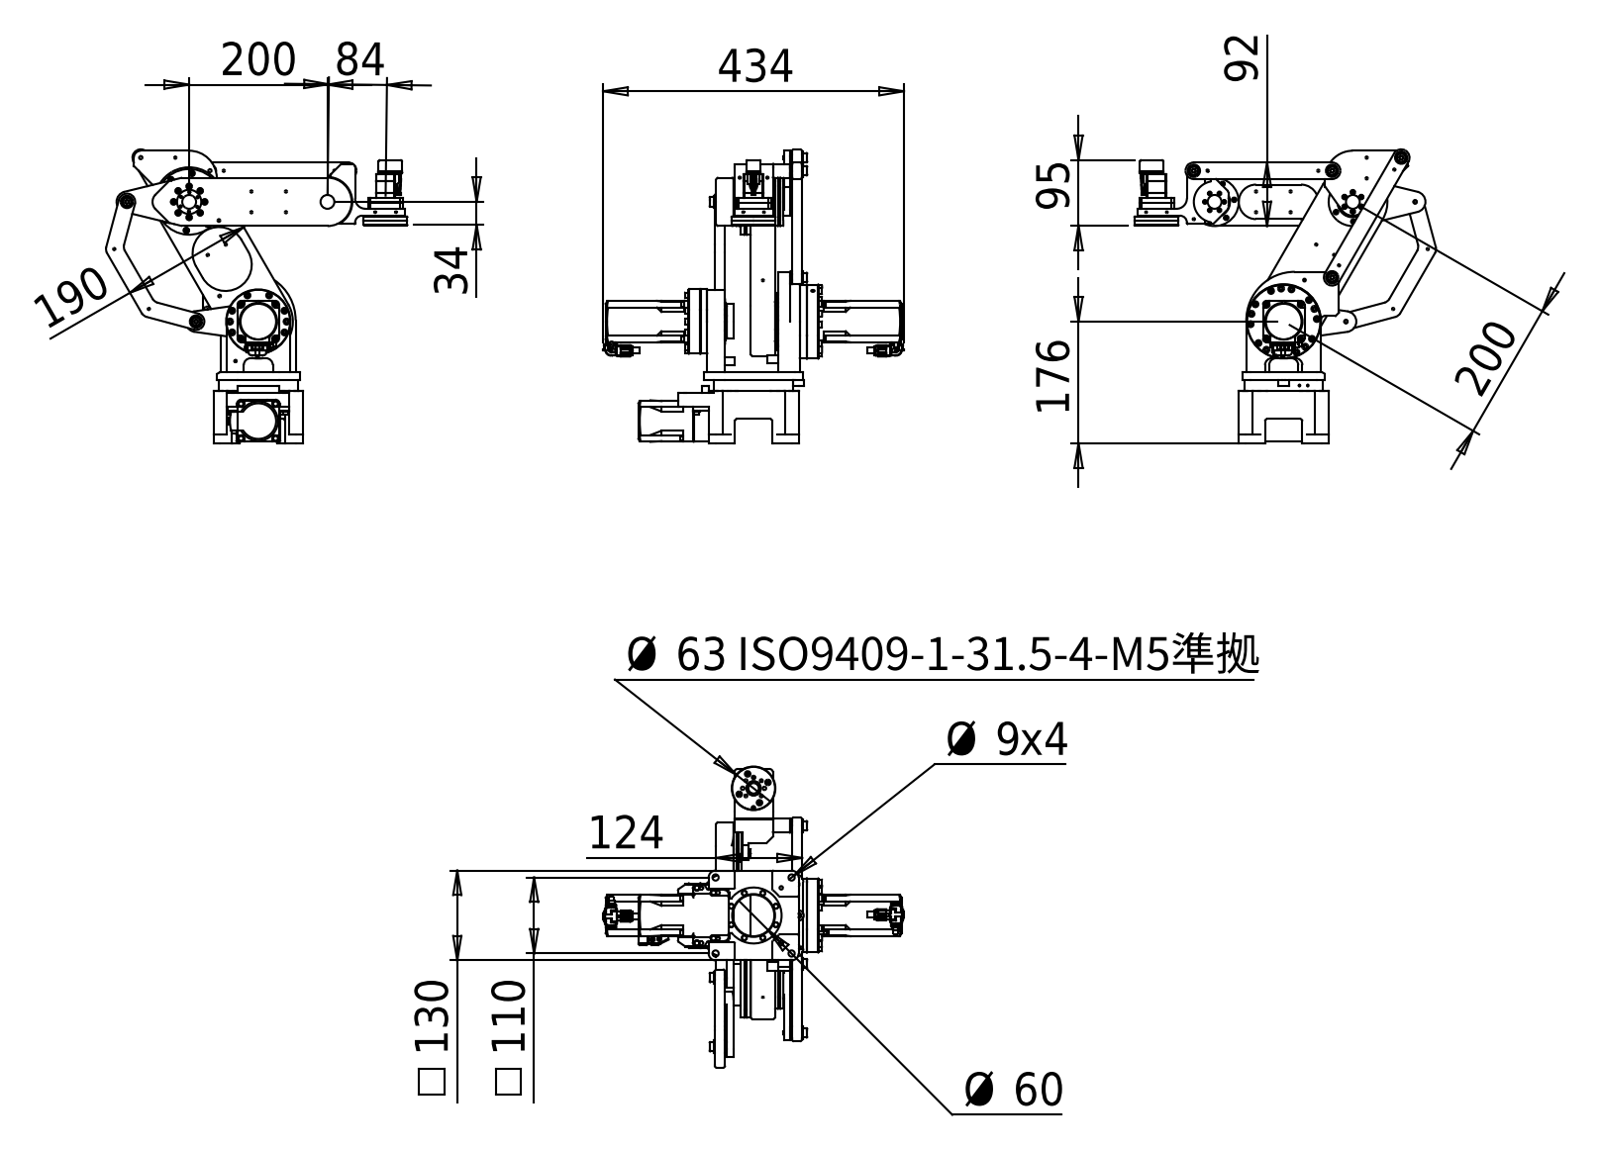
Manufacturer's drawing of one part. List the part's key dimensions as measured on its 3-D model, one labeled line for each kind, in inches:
Part name (STEP PRODUCT): UMBKS12_15_M4_3; SSRBN16_A; CRBFV3515ATUU_61; hexagon socket head cap screw_jis_JIS B 1176 M3 x 12 (12) --N (+8 more)
STEP written by: SolidWorks 2022 (AUTOMOTIVE_DESIGN)
Units: inches
Bodies: 313 solids, 11675 faces (4414 planar, 3799 cylindrical, 3462 other)
Overall size (bounding box): 25.501 × 17.794 × 17.118
Volume: 299.9 in³ · Surface area: 1 573 in²
Round holes (diameter × count): ⌀0.165 ×54, ⌀0.13 ×48, ⌀0.197 ×46, ⌀0.177 ×37, ⌀0.134 ×32, ⌀0.315 ×27, ⌀0.217 ×26, ⌀0.256 ×26, ⌀0.098 ×22, ⌀0.118 ×22, ⌀0.26 ×16, ⌀0.433 ×16
Round bosses / shafts (diameter × count): ⌀0.157 ×79, ⌀0.126 ×48, ⌀0.236 ×43, ⌀0.276 ×40, ⌀0.217 ×34, ⌀0.118 ×34, ⌀0.189 ×26, ⌀0.335 ×22
Partial cylindrical surfaces — rounded edges, fillets, slot ends (radius × count): R0.012 ×98, R0.008 ×73, R0.118 ×46, R0.079 ×42, R0.039 ×41, R0.103 ×23, R0.104 ×23, R0.121 ×23
Main face-to-face distances: 1.378, 2.362, 1.063, 0.984, 0.591, 0.472, 1.969, 2.913, 0.945, 1.535
Hole centre spacings: 0.265, 0.921, 2.047, 0.191, 0.733, 0.831, 1.969, 0.472
